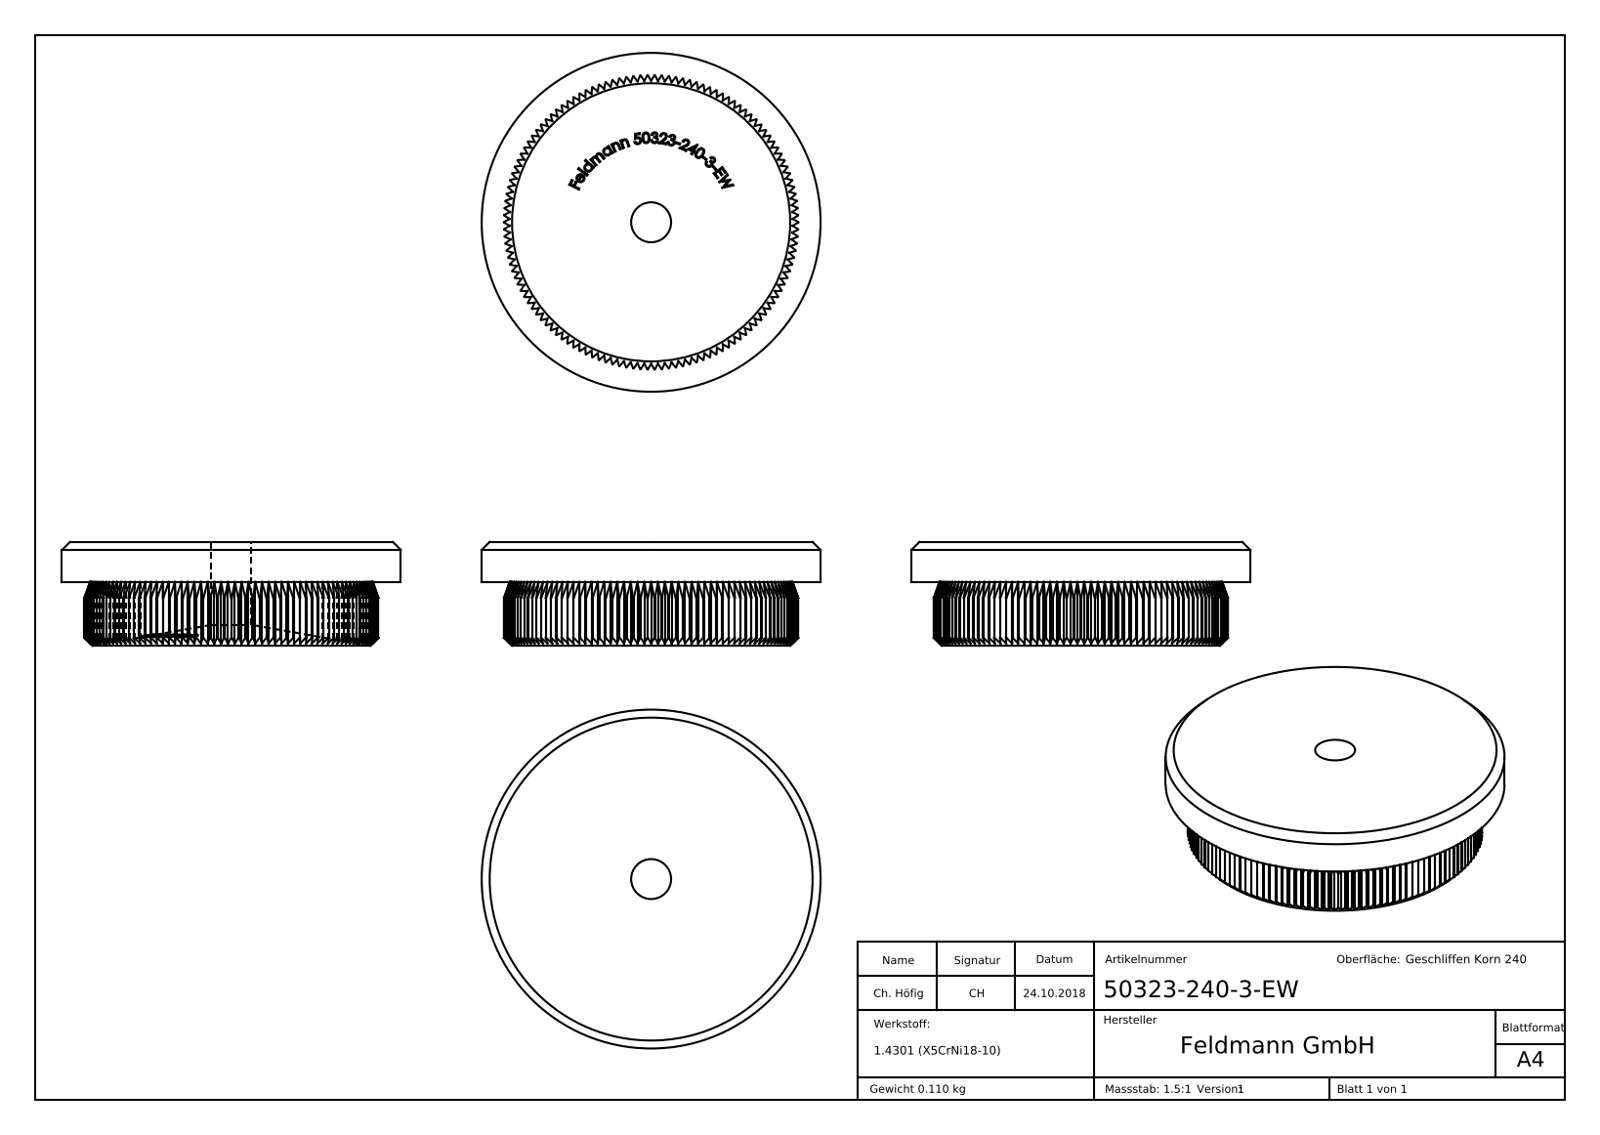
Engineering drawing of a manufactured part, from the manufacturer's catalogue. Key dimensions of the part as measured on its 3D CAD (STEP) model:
Part name (STEP PRODUCT): 50323-240-3-EW
STEP written by: SolidWorks 2015 (CONFIG_CONTROL_DESIGN)
Units: millimetres
Bodies: 1 solid, 826 faces (405 planar, 134 cylindrical, 287 other)
Overall size (bounding box): 42.4 × 42.4 × 13
Volume: 13 976 mm³ · Surface area: 5 148 mm²
Round holes (diameter × count): ⌀5 ×1
Round bosses / shafts (diameter × count): ⌀42.4 ×1
Partial cylindrical surfaces — rounded edges, fillets, slot ends (radius × count): R18.4 ×1
Main face-to-face distances: 17.7, 5, 17.72, 17.68, 0.72, 0.53, 0.66, 1.32, 0.55, 0.6
